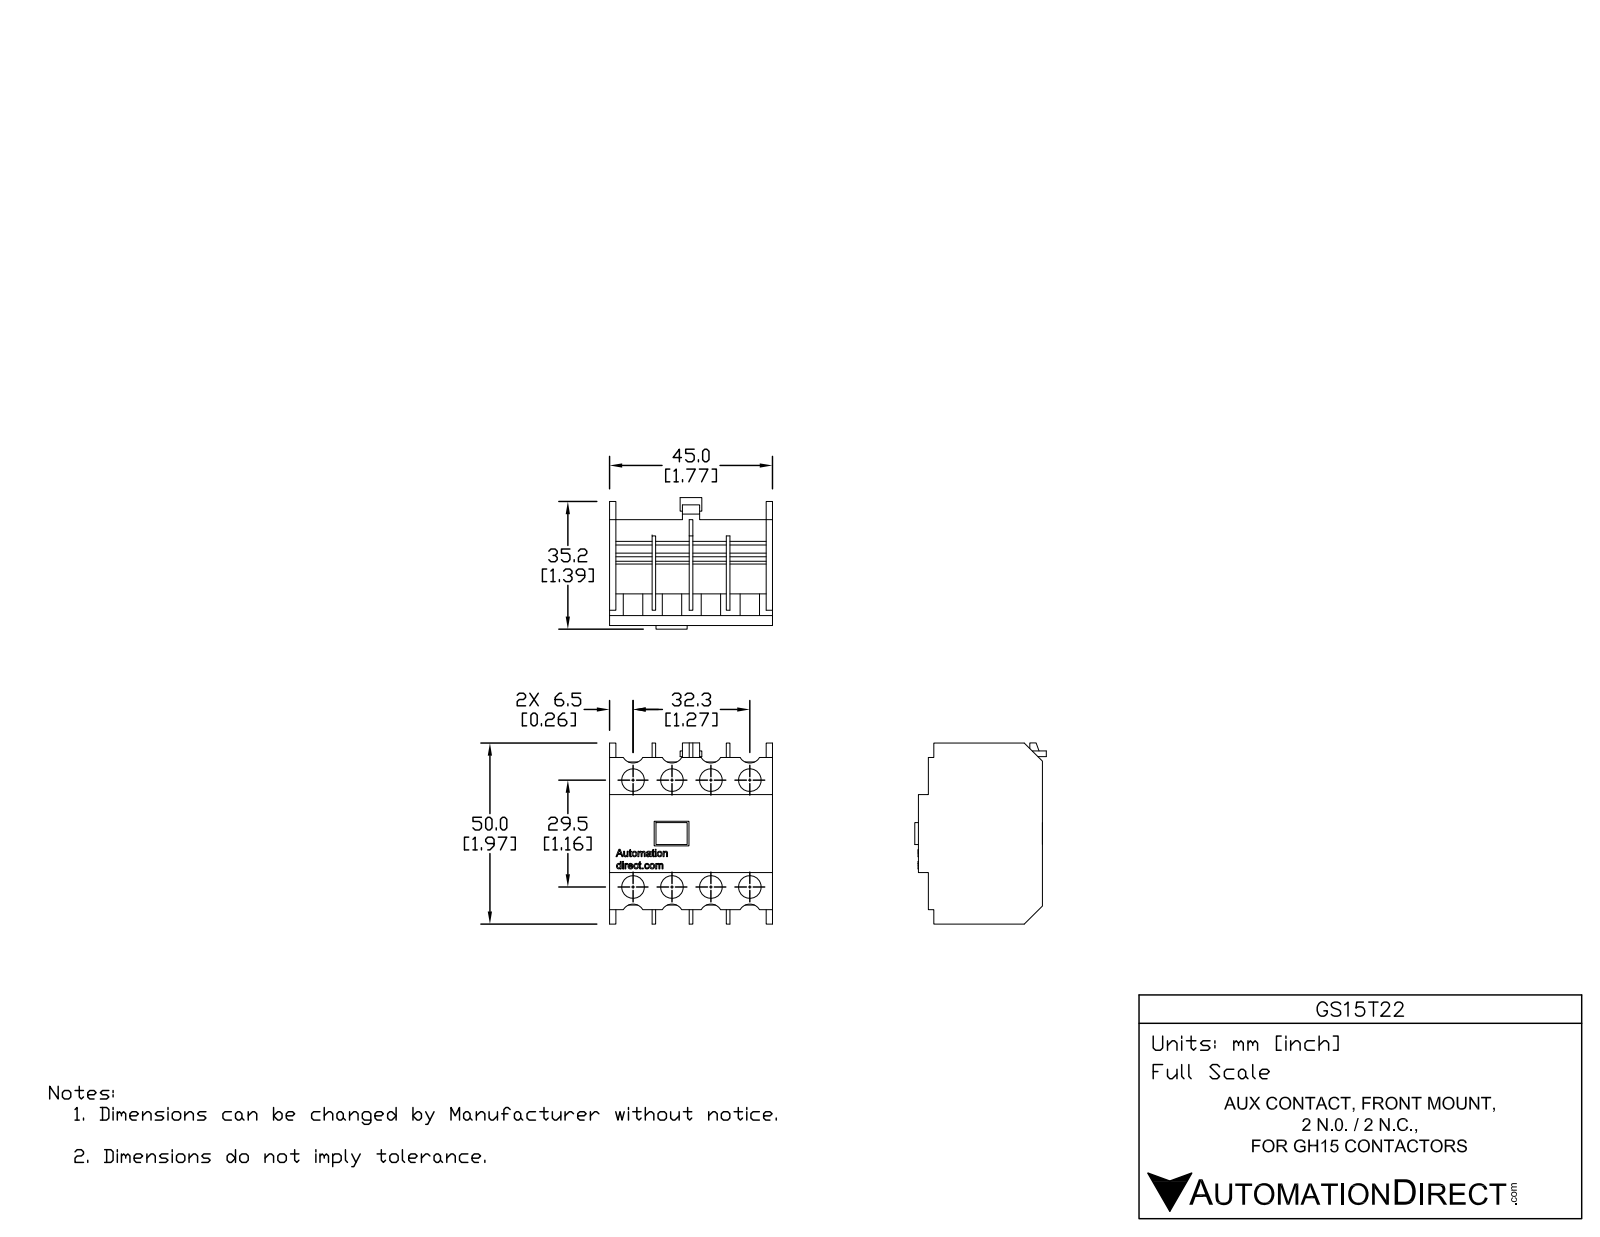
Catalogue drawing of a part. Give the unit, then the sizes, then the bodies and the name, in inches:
Units: inches
Overall size (bounding box): 1.97 × 1.772 × 1.43
Round holes (diameter × count): ⌀0.246 ×8
Partial cylindrical surfaces — rounded edges, fillets, slot ends (radius × count): R0.123 ×8
Main face-to-face distances: 0.404, 0.807, 1.772, 0.069, 1.703, 0.039, 0.236, 0.866, 0.561, 0.502
Hole centre spacings: 0.423, 1.236, 0.846, 1.161, 1.437, 1.27, 1.721
Volume: 2.372 in³ · Surface area: 26.11 in²
Bodies: 1 solid, 509 faces (359 planar, 24 cylindrical, 126 other)
Part name (STEP PRODUCT): GH15T22
STEP written by: SolidWorks 2009 (CONFIG_CONTROL_DESIGN)
